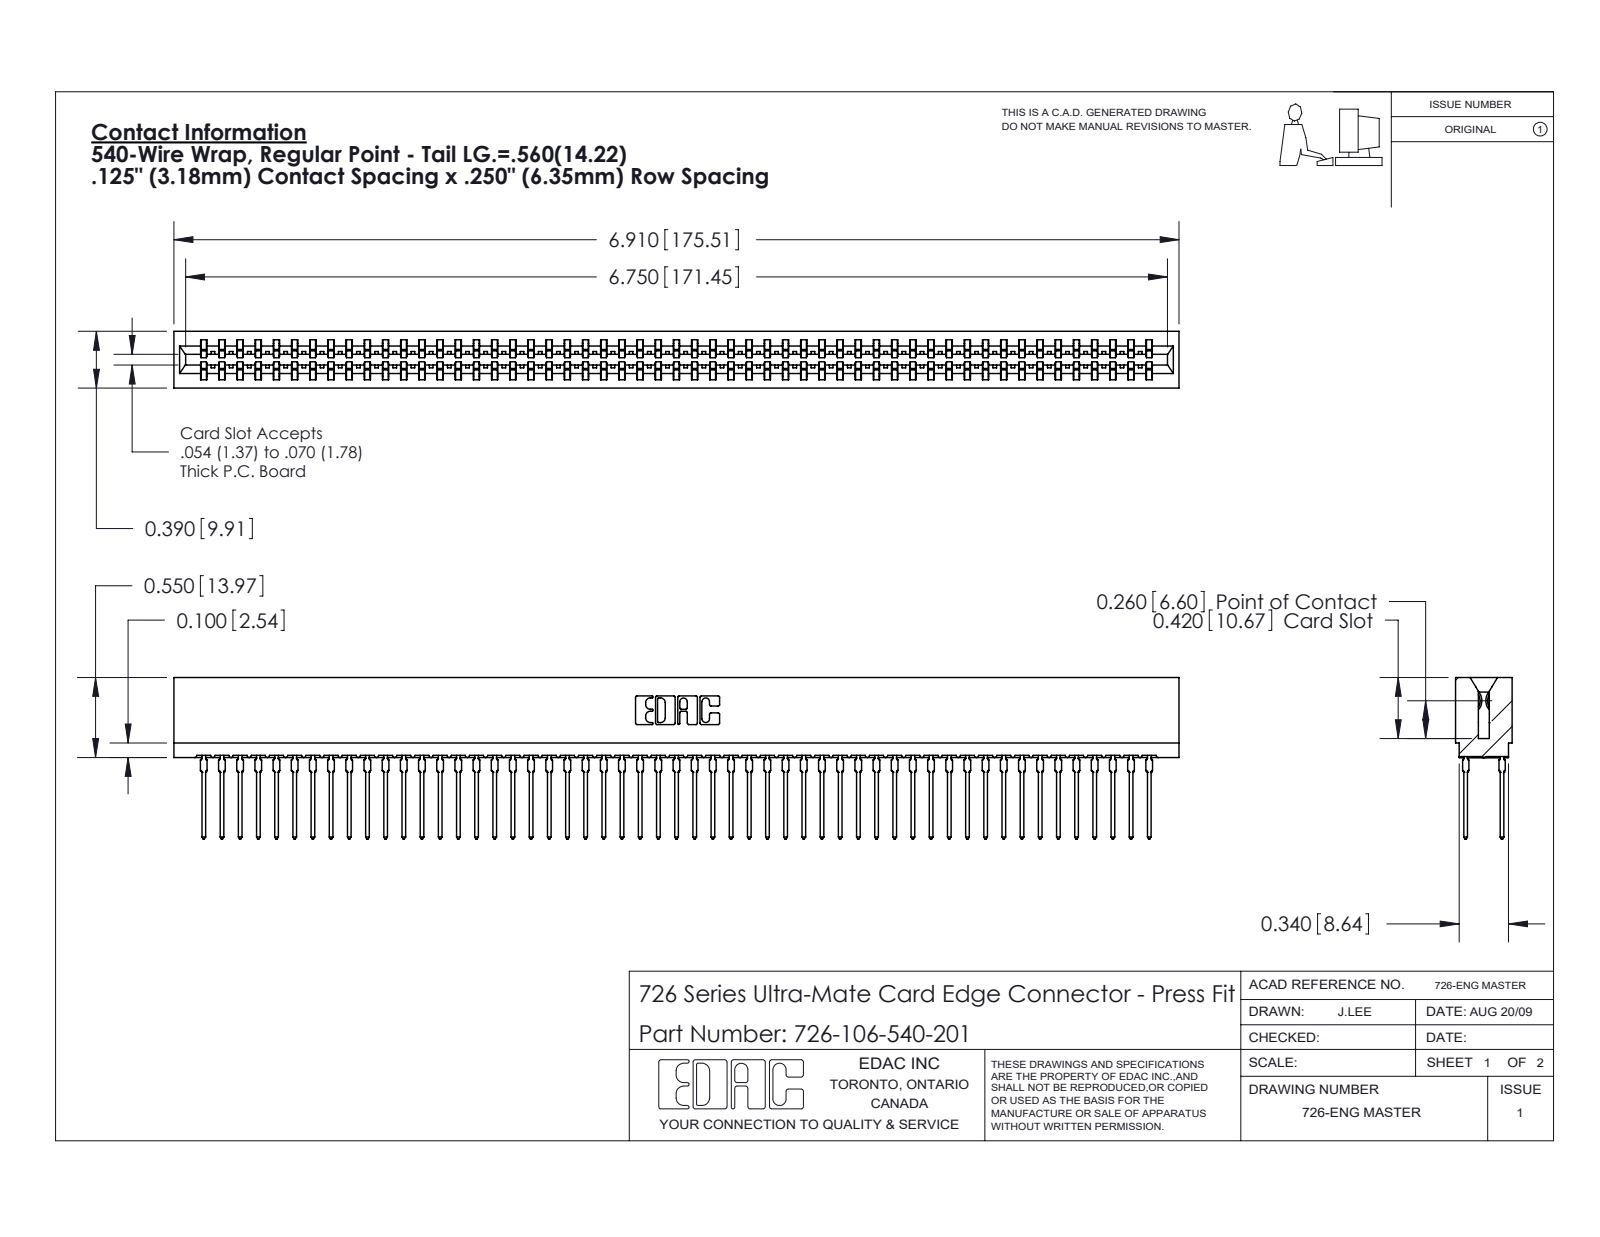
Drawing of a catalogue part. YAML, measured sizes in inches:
part_name: "726-106-540-201; 746-292-001_540; 726 Part_.515 Slot Depth - 01"
step_written_by: "SolidWorks 2020 (CONFIG_CONTROL_DESIGN)"
units: inches
bodies: {solids: 106, faces: 9584, planar: 4931, cylindrical: 1897, other: 2756}
overall_size: [6.91, 1.109, 0.39]
volume: 0.084
surface_area: 45
partial_cylinders:
  - {radius: 0.021, count: 212}
  - {radius: 0.015, count: 54}
  - {radius: 0.01, count: 22}
  - {radius: 0.005, count: 8}
  - {radius: 0.011, count: 8}
  - {radius: 0.007, count: 6}
  - {radius: 0.031, count: 6}
  - {radius: 0.026, count: 3}
face_to_face_distances: [0.057, 0.333, 0.025, 0.307, 0.25, 0.39, 0.083, 0.275, 0.365, 0.032]
